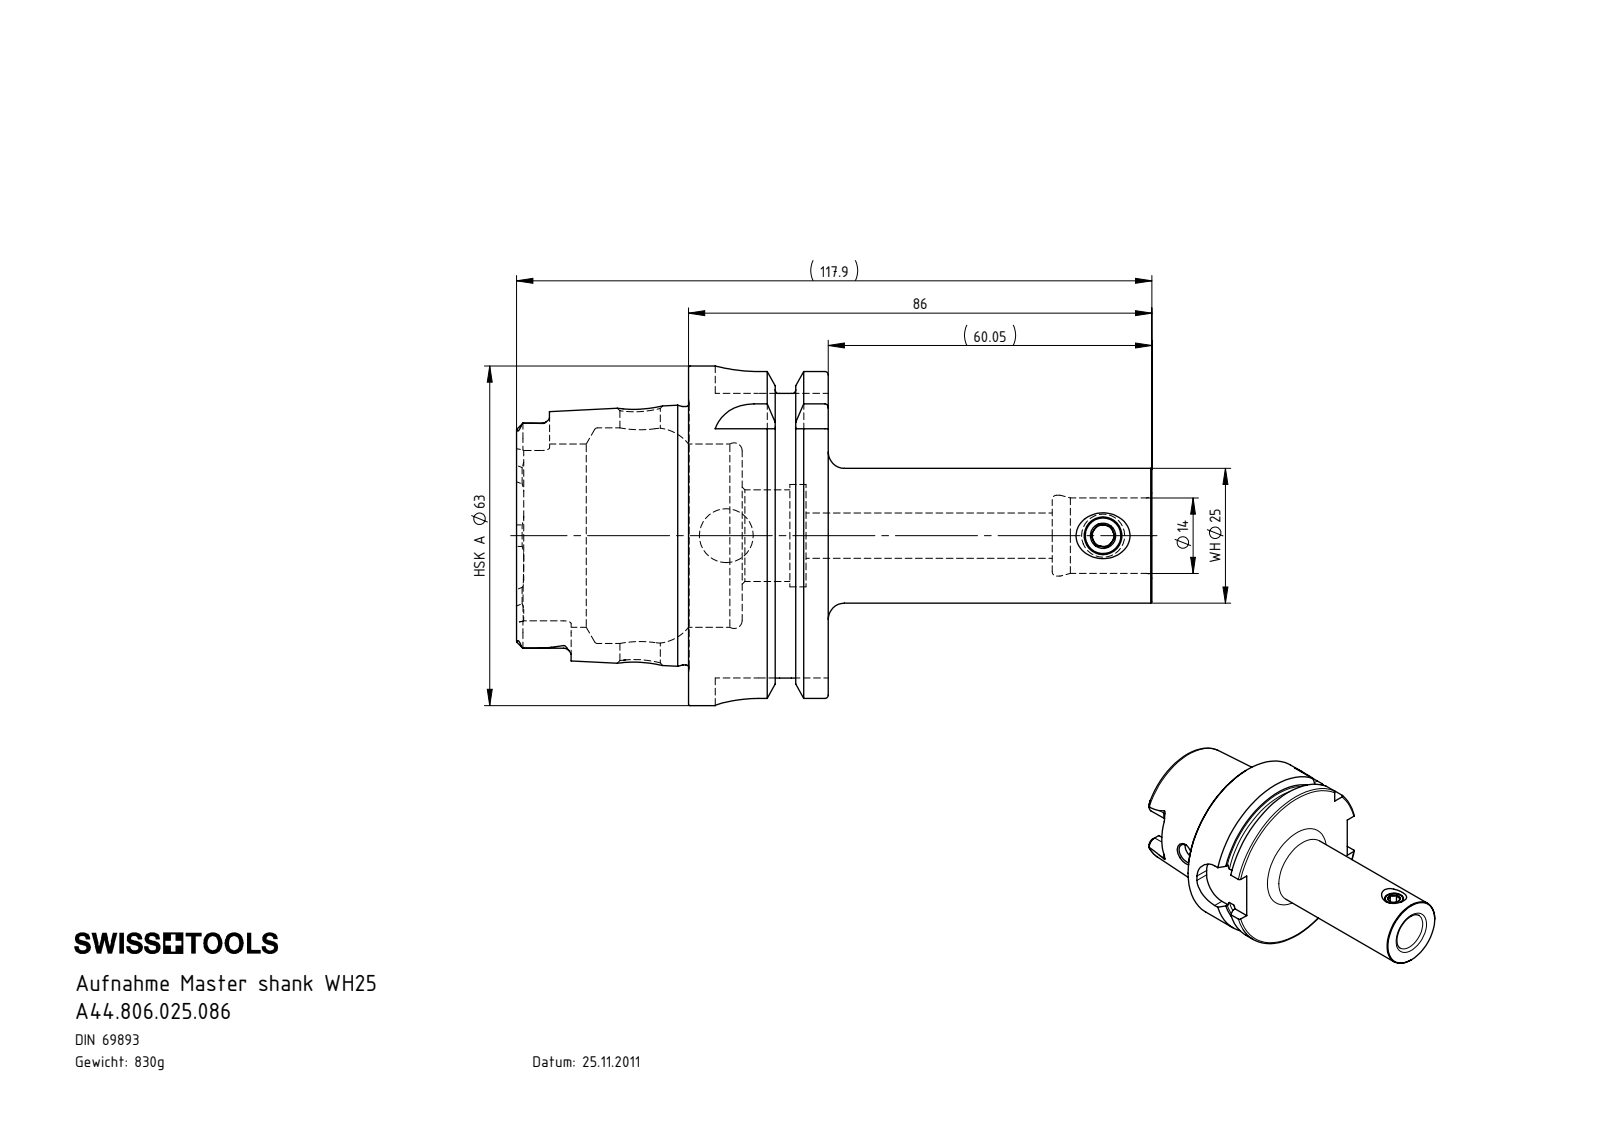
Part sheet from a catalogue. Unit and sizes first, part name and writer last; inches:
Units: inches
Overall size (bounding box): 4.642 × 2.48 × 2.48
Round holes (diameter × count): ⌀0.157 ×1, ⌀0.276 ×1, ⌀0.295 ×1, ⌀0.331 ×1, ⌀0.394 ×1, ⌀0.551 ×1, ⌀0.591 ×1, ⌀0.669 ×1, ⌀0.748 ×1, ⌀1.339 ×1, ⌀1.575 ×1
Round bosses / shafts (diameter × count): ⌀2.48 ×1, ⌀2.163 ×1, ⌀1.887 ×1, ⌀0.984 ×1, ⌀0.315 ×1
Partial cylindrical surfaces — rounded edges, fillets, slot ends (radius × count): R0.055 ×6, R0.113 ×4, R0.315 ×4
Main face-to-face distances: 1.022, 0.63, 0.392, 1.256, 1.648, 2.278, 2.079, 0.858, 4.642, 3.386
Hole centre spacings: 2.754
Volume: 6.587 in³ · Surface area: 45.21 in²
Bodies: 2 solids, 211 faces (61 planar, 55 cylindrical, 95 other)
Part name (STEP PRODUCT): A44.806.025.086; WH2-ER1.001.008; HA6-WH2.K01.086_C
STEP written by: SolidWorks 2017 (CONFIG_CONTROL_DESIGN)
